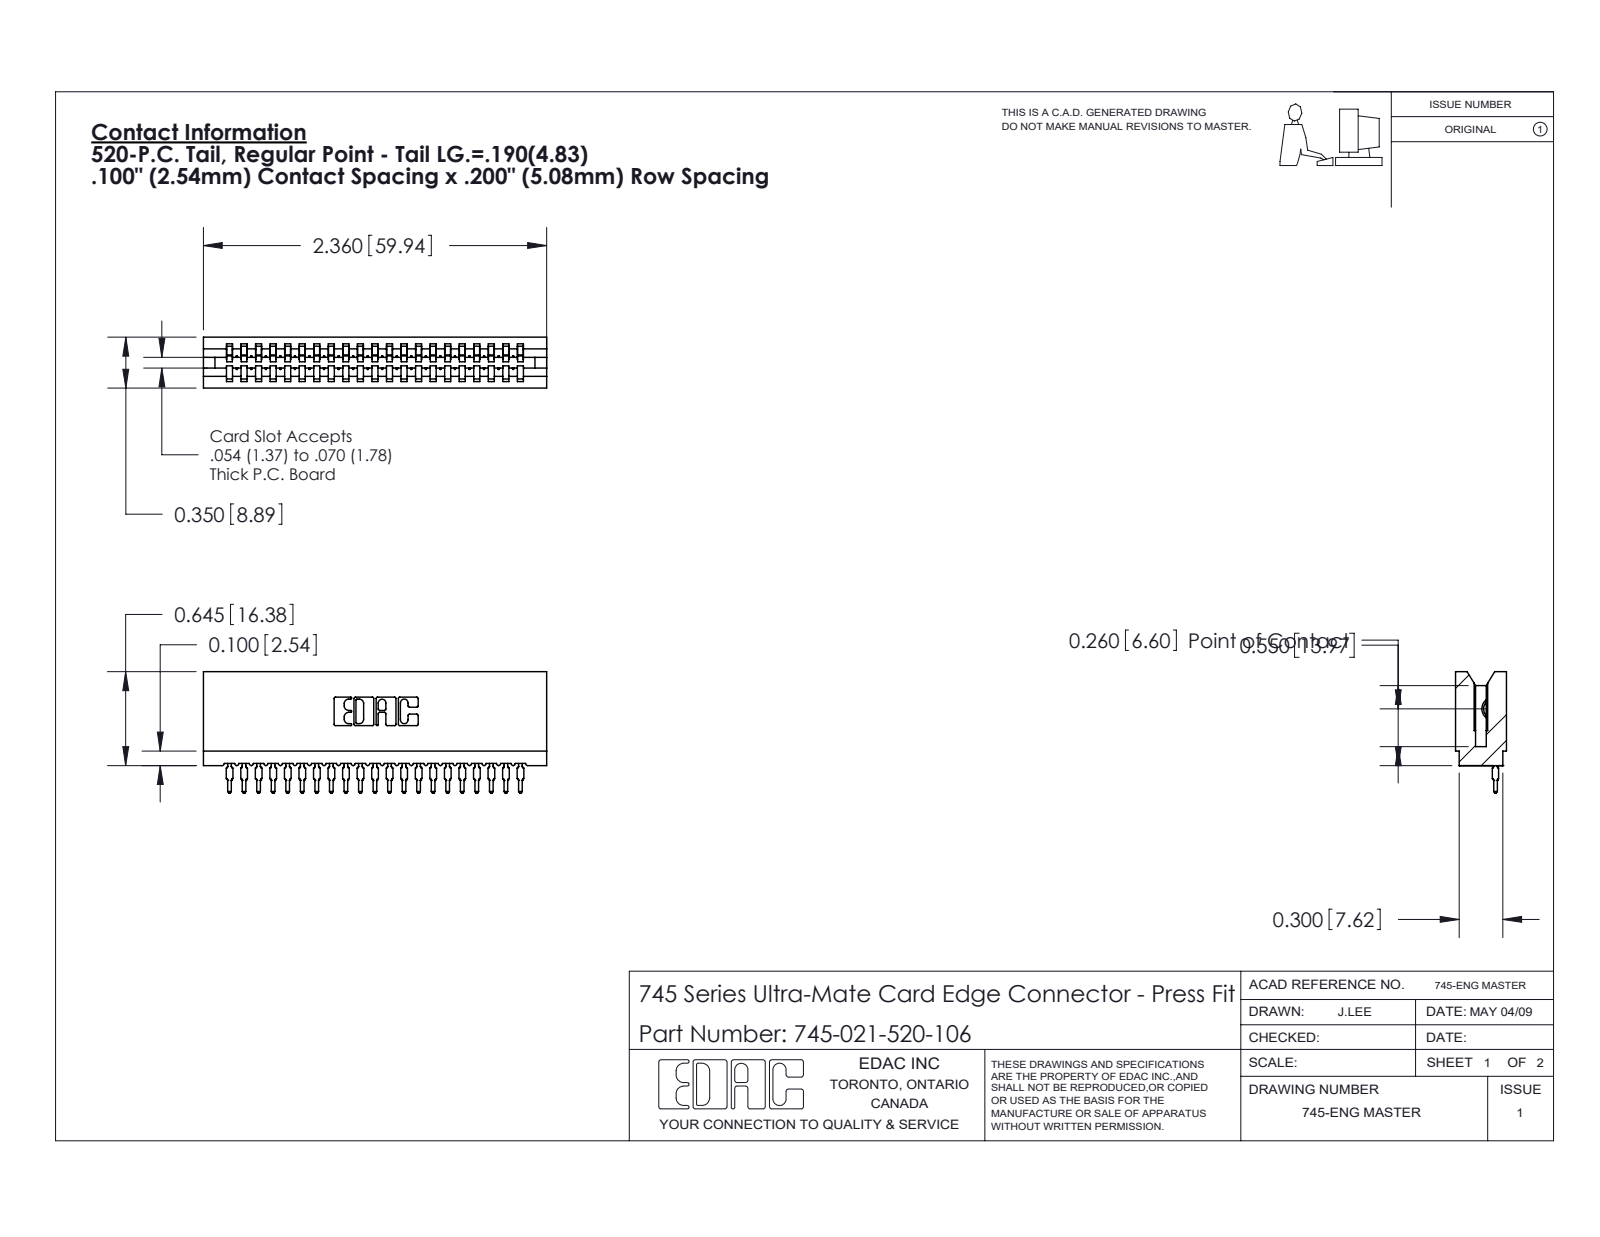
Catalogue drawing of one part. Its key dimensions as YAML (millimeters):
part_name: "745-292-001_520; 745 Part_Insulator Option - 06; 745-021-520-106"
step_written_by: "SolidWorks 2020 (CONFIG_CONTROL_DESIGN)"
units: millimeters
bodies: {solids: 22, faces: 2448, planar: 1463, cylindrical: 439, other: 546}
overall_size: [59.9, 21.2, 8.9]
volume: 5280
surface_area: 9323
partial_cylinders:
  - {radius: 0.4, count: 42}
  - {radius: 0.5, count: 42}
  - {radius: 0.3, count: 22}
  - {radius: 0.2, count: 6}
  - {radius: 0.8, count: 6}
  - {radius: 0.1, count: 4}
  - {radius: 0.3, count: 4}
  - {radius: 0.7, count: 3}
face_to_face_distances: [2.5, 5.1, 7.6, 10.2, 8.9, 12.7, 15.2, 17.8, 3.5, 5.4]
